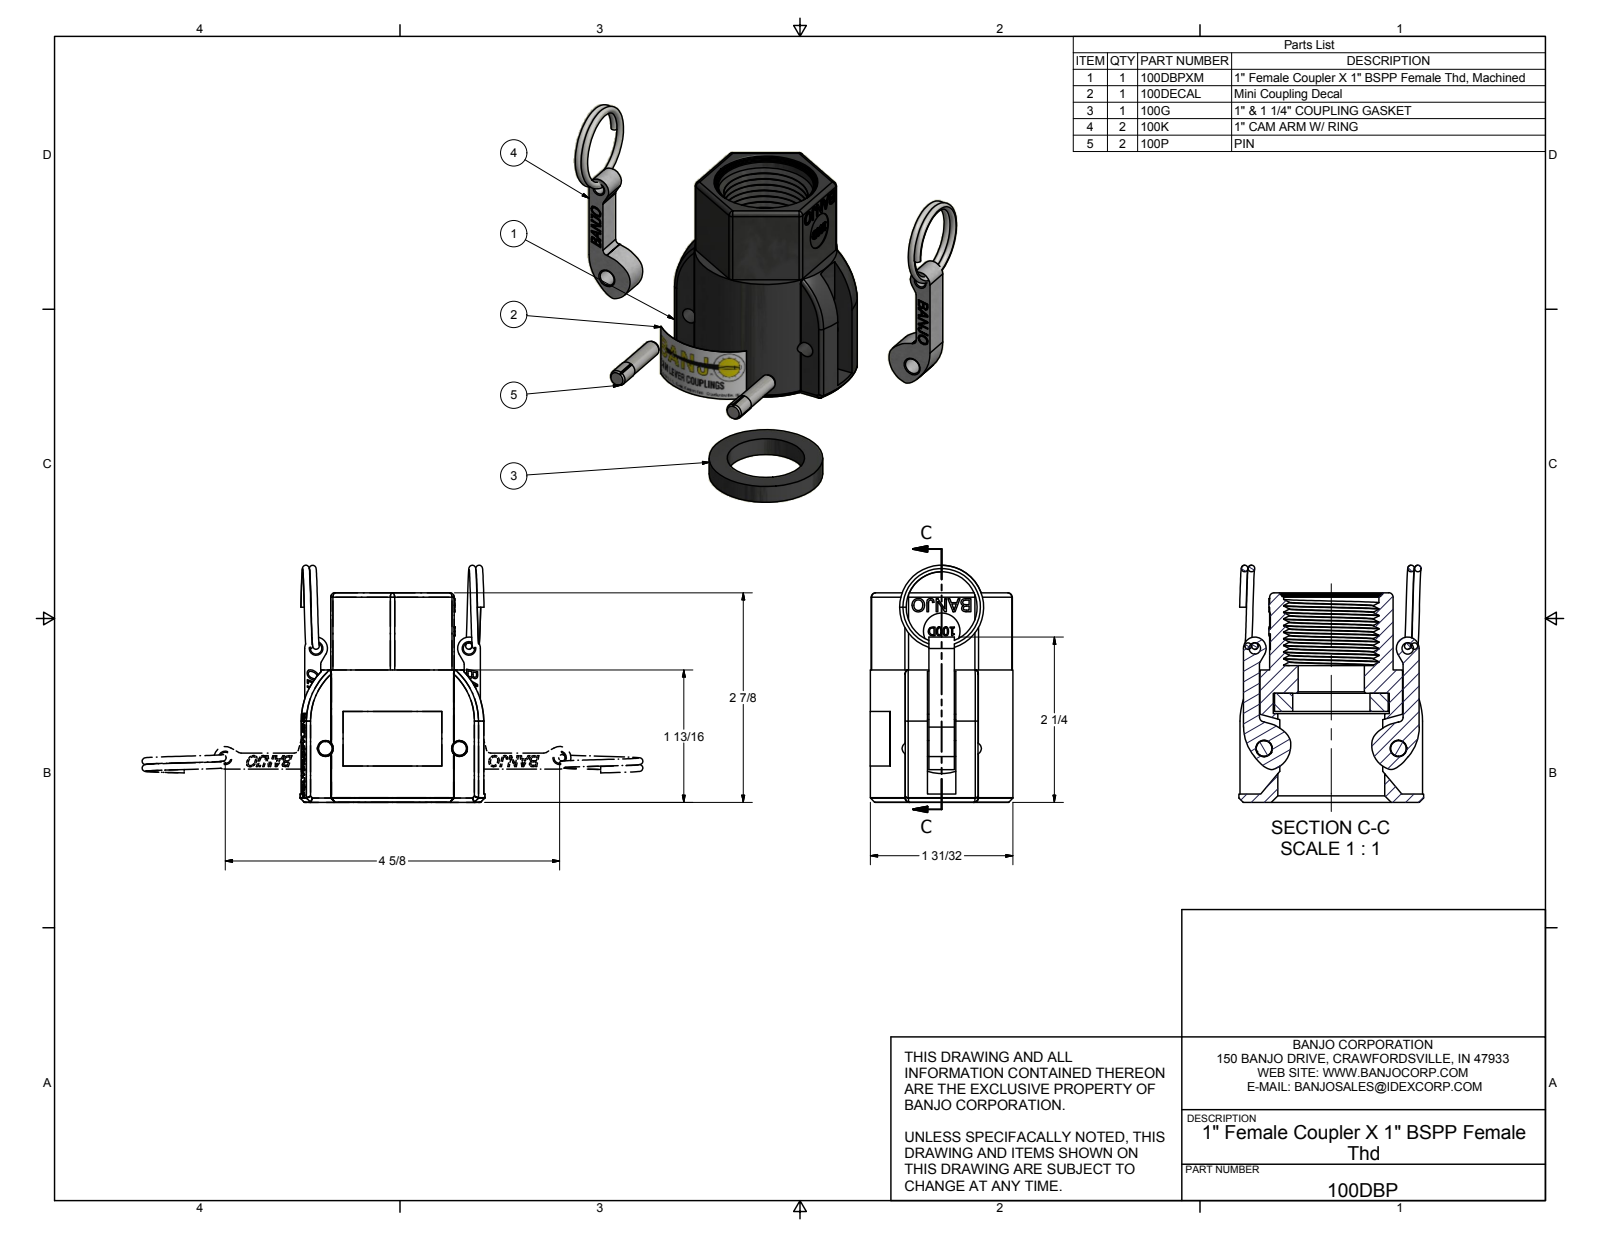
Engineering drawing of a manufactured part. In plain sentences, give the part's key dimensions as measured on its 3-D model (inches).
The part is named "100DBPX; 100DBPXM; 100G; 100P (+5 more)". Its 3-D file was written by "Autodesk Inventor 2014 (AUTOMOTIVE_DESIGN)". It is 9 solids with 967 faces: 450 planar, 107 cylindrical and 410 other. Overall it measures 3.259 by 2.54 by 1.963 inches. Its volume is 5.174 cubic inches and its surface area 60.1 square inches. Round holes: 2 of diameter 0.156, 2 of diameter 0.219, 2 of diameter 0.225, 1 of diameter 0.5, 1 of diameter 0.91, 1 of diameter 1.063, 1 of diameter 1.158, 1 of diameter 1.309, 1 of diameter 1.359, 1 of diameter 1.409, 1 of diameter 1.47, 1 of diameter 1.594. Round bosses or shafts: 2 of diameter 0.227, 2 of diameter 0.217, 1 of diameter 1.563. Partial cylindrical surfaces (rounded edges, fillets, slot ends): 18 of radius 0.06, 4 of radius 0.01, 2 of radius 0.063, 2 of radius 0.063, 2 of radius 0.156, 2 of radius 0.625, 1 of radius 0.403, 1 of radius 0.98. The main face-to-face distances are 1.698, 0.305, 0.695, 1, 0.39, 0.35, 0.02, 0.25, 1.25, 1.5. The hole center spacings are 1.381, 2.406, 1.847, 2.102.
